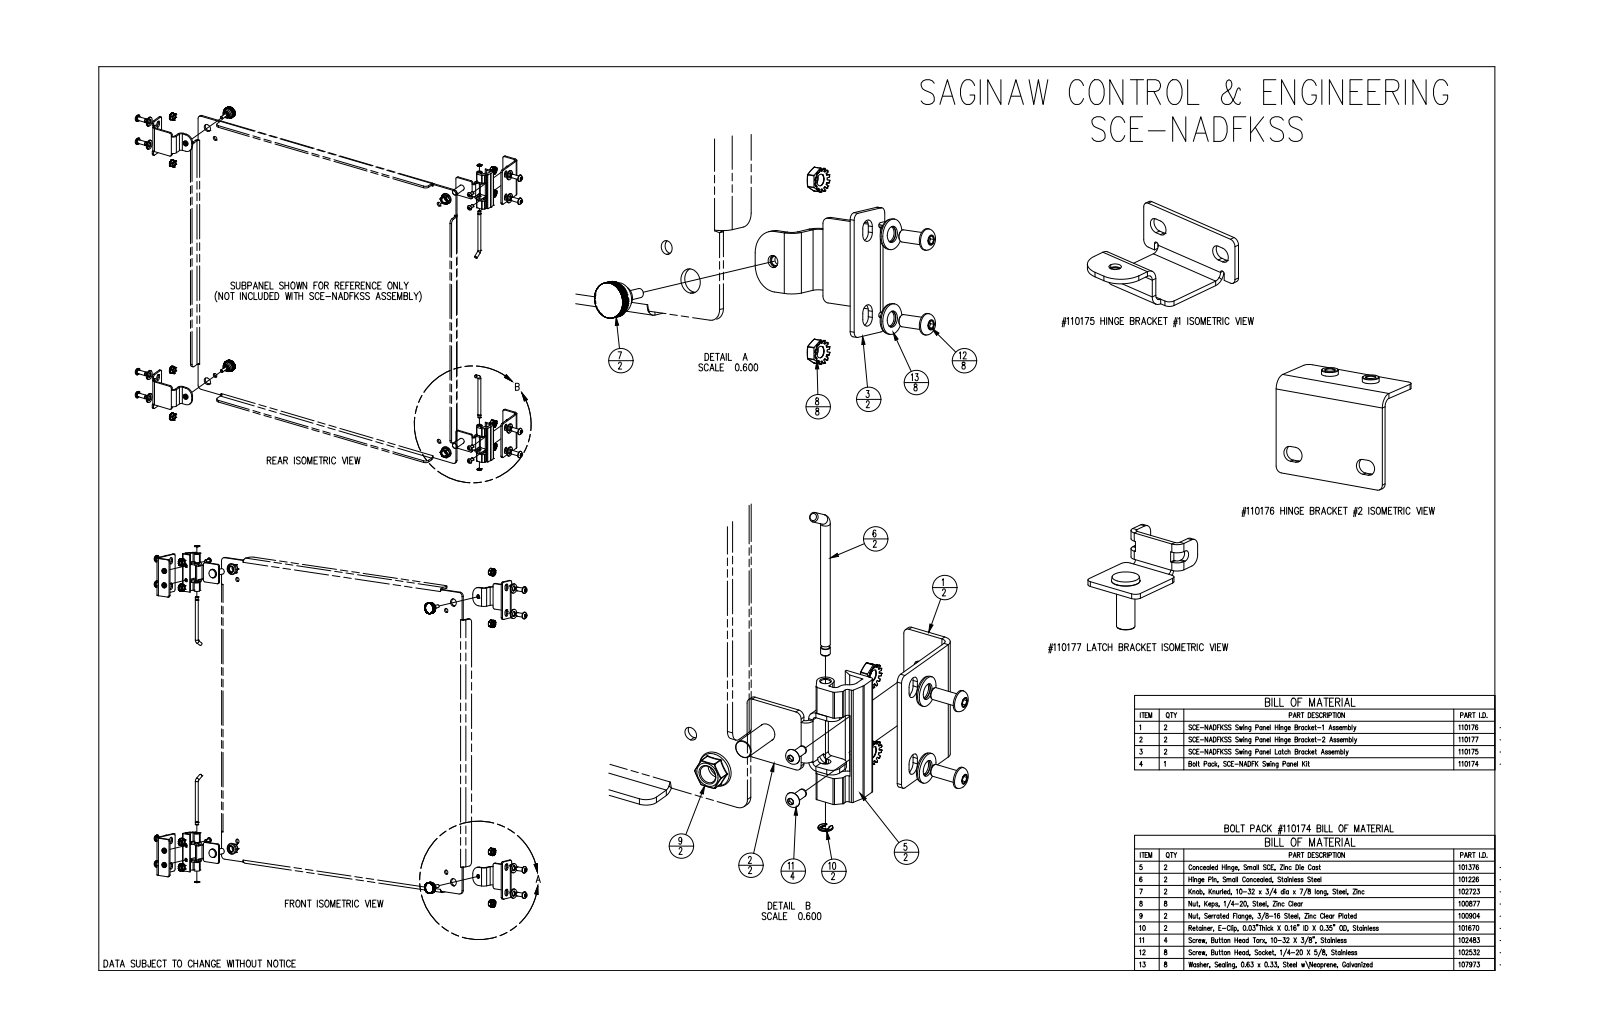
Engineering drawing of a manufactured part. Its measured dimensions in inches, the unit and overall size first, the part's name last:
Units: inches
Overall size (bounding box): 24.288 × 22.339 × 2.408
Round holes (diameter × count): ⌀0.25 ×14, ⌀0.31 ×8, ⌀0.33 ×8, ⌀0.19 ×6, ⌀0.205 ×4, ⌀0.281 ×4, ⌀0.5 ×4, ⌀0.367 ×2, ⌀0.375 ×2, ⌀0.203 ×1
Round bosses / shafts (diameter × count): ⌀0.625 ×8, ⌀0.6 ×8, ⌀0.437 ×8, ⌀0.34 ×6, ⌀0.249 ×6, ⌀0.17 ×4, ⌀0.196 ×3, ⌀0.623 ×2
Partial cylindrical surfaces — rounded edges, fillets, slot ends (radius × count): R0.01 ×66, R0.005 ×48, R0.125 ×25, R0.156 ×16, R0.13 ×8, R0.25 ×8, R0.068 ×6, R0.07 ×5
Main face-to-face distances: 0.125, 0.125, 20.875, 0.104, 20.75, 21, 1.461, 1.586, 22.335, 22.461
Hole centre spacings: 18.641, 19.25, 20.801, 19.25, 0.033, 0.875, 0.985, 1.622
Volume: 67.02 in³ · Surface area: 1 118 in²
Bodies: 61 solids, 3266 faces (1860 planar, 746 cylindrical, 660 other)
Part name (STEP PRODUCT): SCE-NADFKSS
STEP written by: SolidWorks 2019 (CONFIG_CONTROL_DESIGN)
